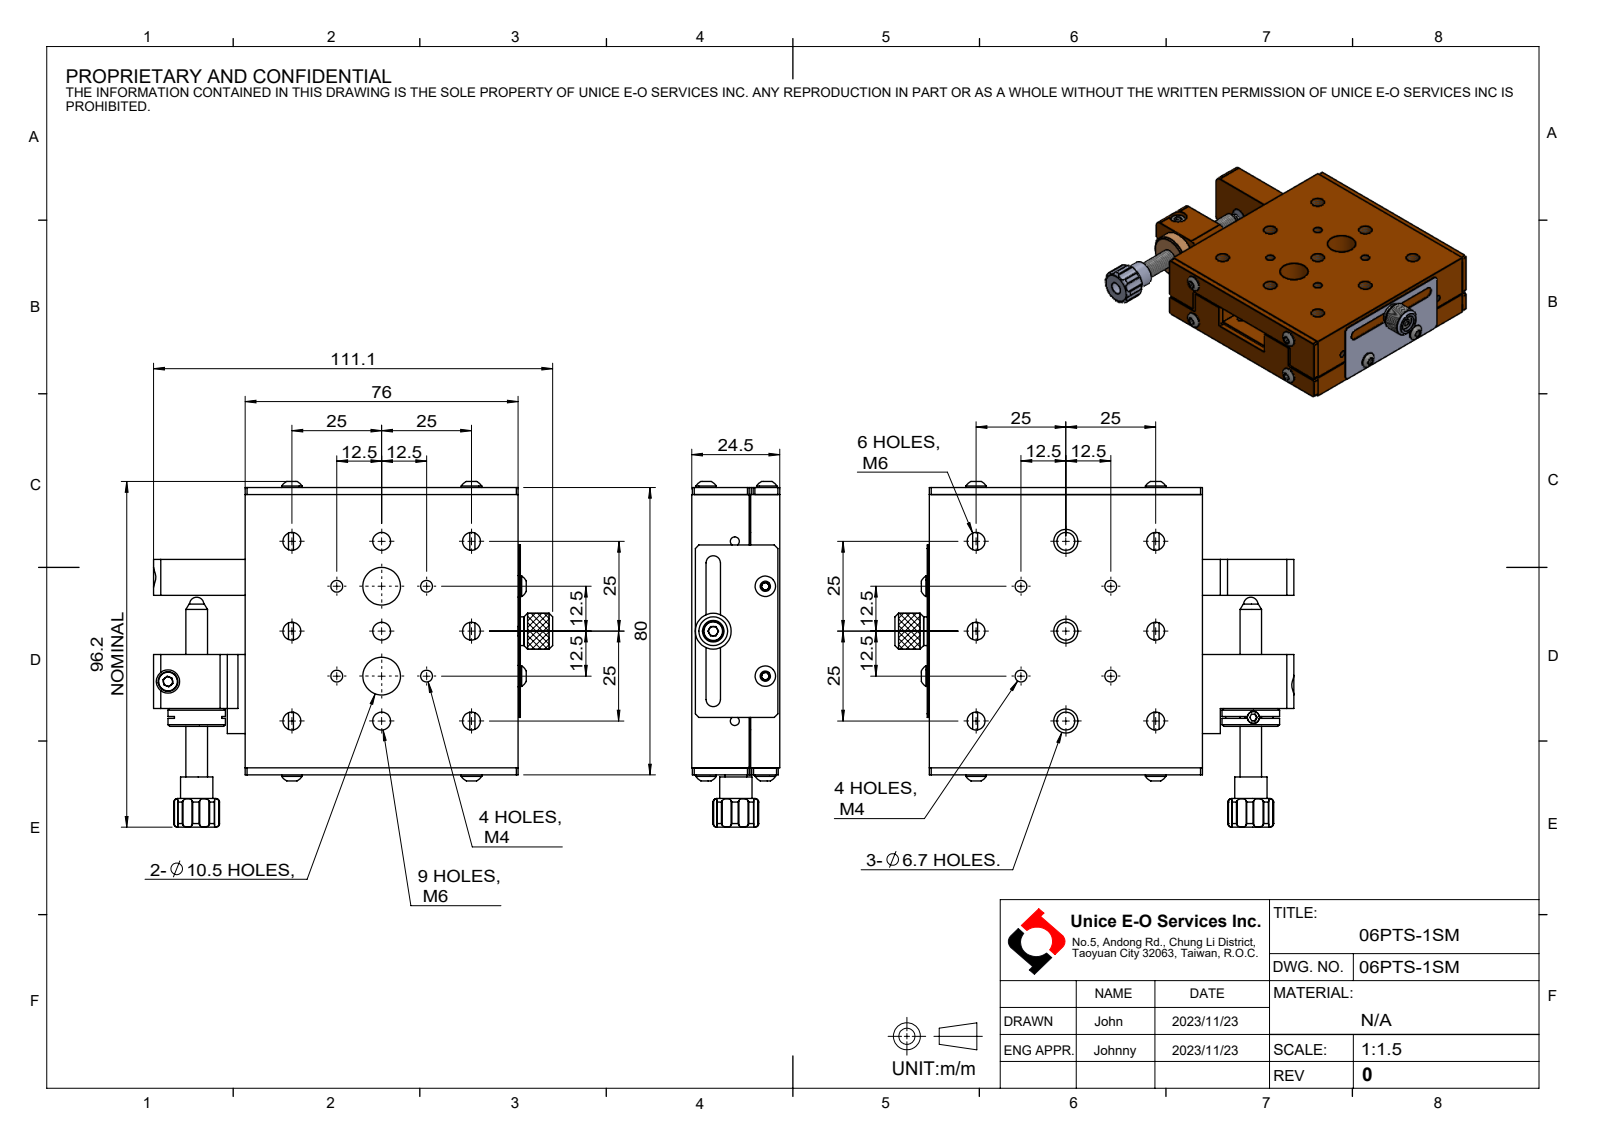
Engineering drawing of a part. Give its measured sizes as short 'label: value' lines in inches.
name: 06PTS-1SM
written by: SolidWorks 2016 (CONFIG_CONTROL_DESIGN)
unit: in
bodies: 40 solids, 2012 faces (500 planar, 712 cylindrical, 800 other)
size: 4.374 × 3.798 × 0.965
volume: 8.167 in³; area: 117.7 in²
holes: 39× ⌀0.098, 14× ⌀0.138, 14× ⌀0.236, 13× ⌀0.13, 10× ⌀0.177, 10× ⌀0.197, 4× ⌀0.134, 4× ⌀0.256, 3× ⌀0.264, 2× ⌀0.126, 2× ⌀0.413, 1× ⌀0.157
bosses: 13× ⌀0.118, 8× ⌀0.224, 5× ⌀0.217, 4× ⌀0.024, 3× ⌀0.236, 1× ⌀0.63, 1× ⌀0.394, 1× ⌀0.354
rounds: 32× R0.02, 16× R0.012, 8× R0.079, 8× R0.108, 1× R0.118, 1× R0.25
face distances: 0.323, 0.315, 0.327, 0.319, 0.646, 0.965, 0.65, 2.992, 0.642, 0.311
hole spacings: 0.984, 1.969, 0.696, 1.556, 0.394, 0.759, 0.787, 1.021
